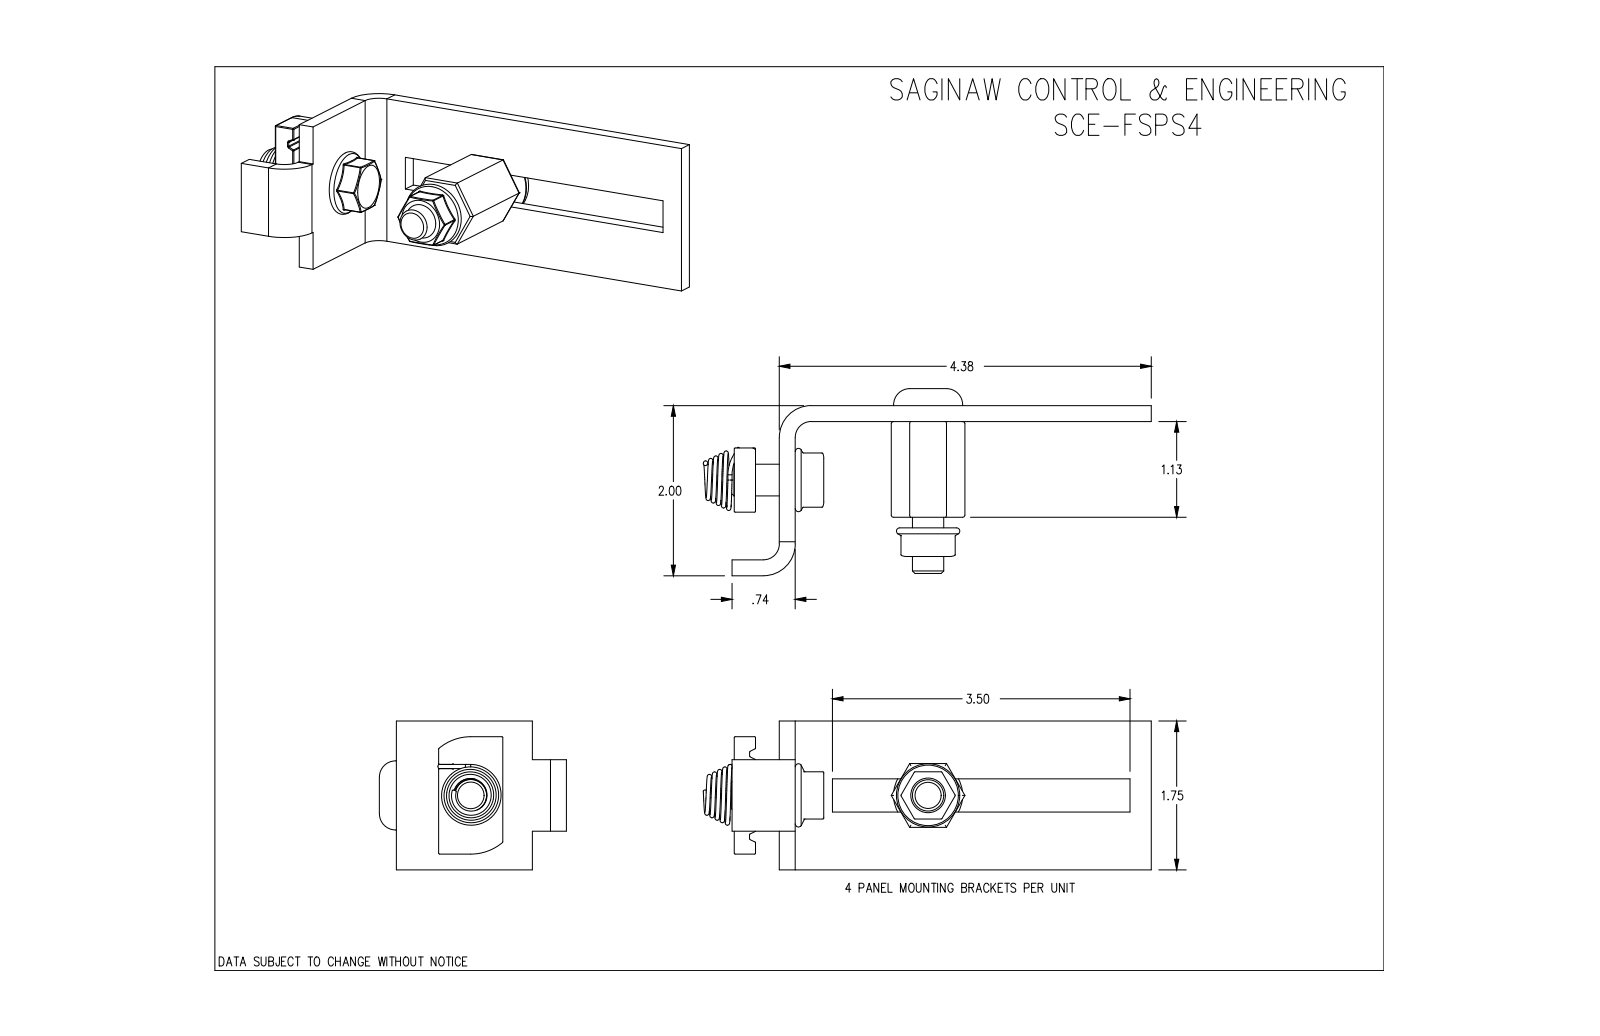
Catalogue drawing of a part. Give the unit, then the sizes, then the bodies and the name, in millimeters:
Units: millimetres
Overall size (bounding box): 1207.5 × 784.2 × 55.9
Round holes (diameter × count): ⌀9.3 ×4, ⌀9.5 ×4, ⌀9.5 ×4
Round bosses / shafts (diameter × count): ⌀1.2 ×8, ⌀20.7 ×4, ⌀9.3 ×4, ⌀9.5 ×2
Partial cylindrical surfaces — rounded edges, fillets, slot ends (radius × count): R0.3 ×176, R0.6 ×40, R1.2 ×16, R4.7 ×4, R9.5 ×4, R14.7 ×4, R4.7 ×2, R4.8 ×2
Main face-to-face distances: 4.7, 1157.3, 17.3, 19.1, 739.8, 739.8, 1152.6, 1162.1, 12.7, 4.6
Hole centre spacings: 739.8, 1073.2, 1303.4
Volume: 190 400 mm³ · Surface area: 102 800 mm²
Bodies: 24 solids, 1088 faces (300 planar, 360 cylindrical, 428 other)
Part name (STEP PRODUCT): SCE-FSPS4
STEP written by: SolidWorks 2019 (CONFIG_CONTROL_DESIGN)
